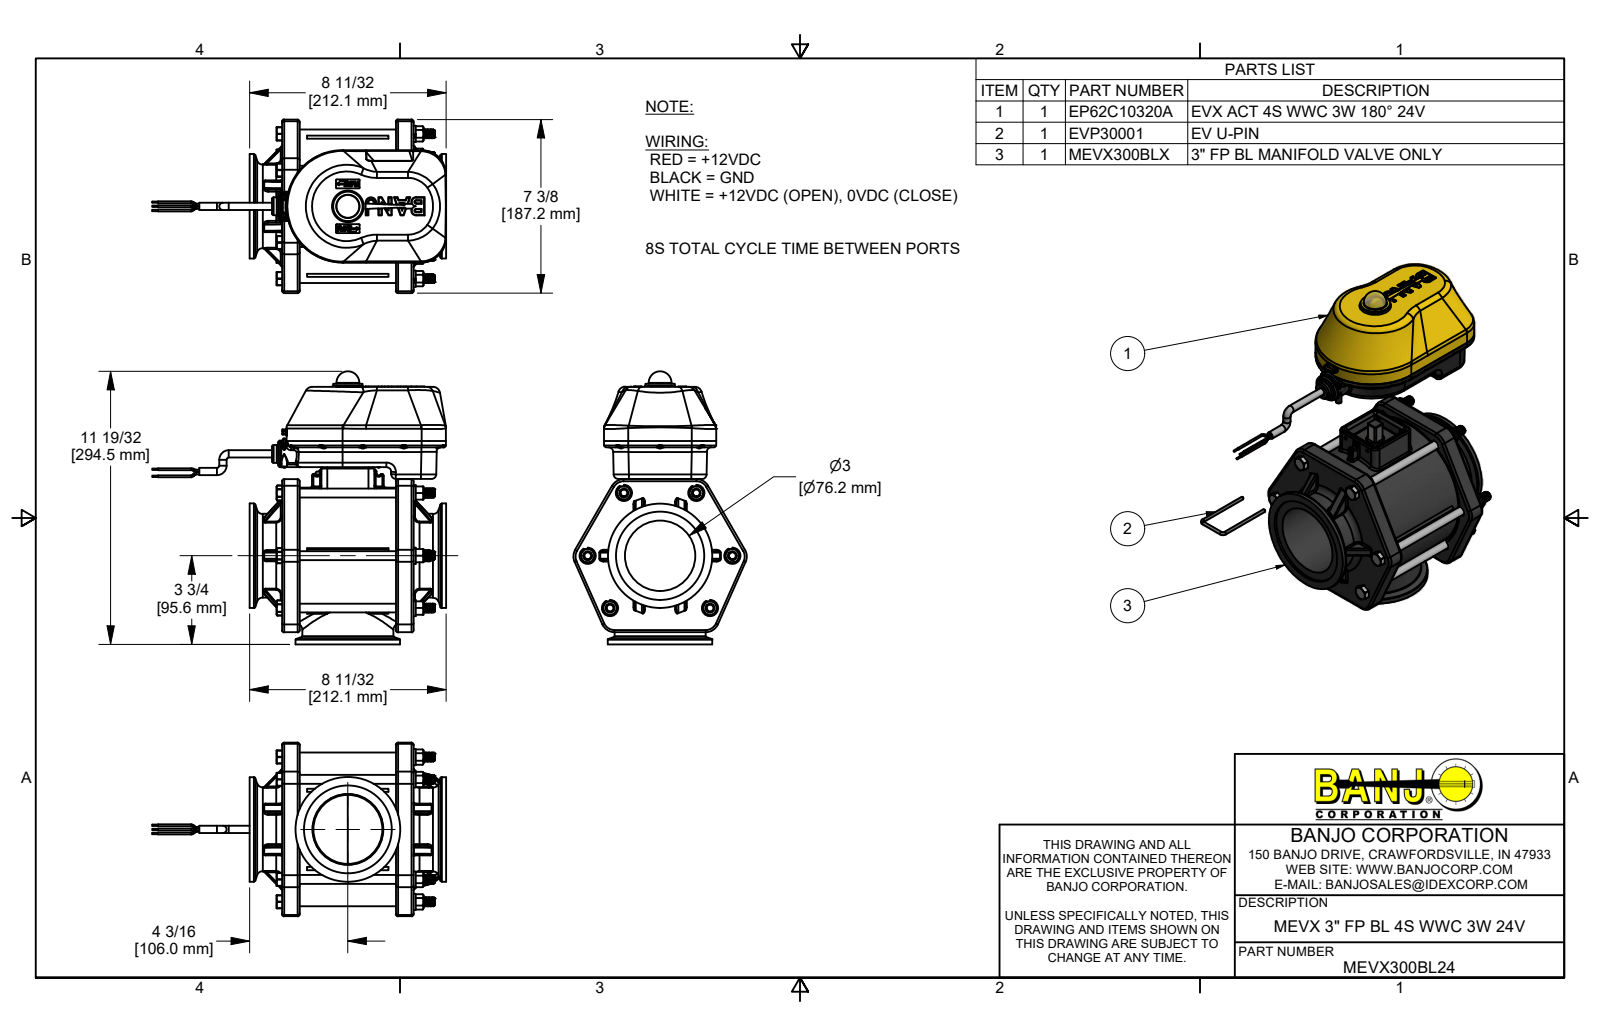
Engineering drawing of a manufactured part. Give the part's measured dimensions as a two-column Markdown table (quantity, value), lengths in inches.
| quantity | value |
| --- | --- |
| part name | MEVX300BL24; MEVX300BLX; MEVX35254BL; MEVX35254BLX (+8 more) |
| STEP written by | Autodesk Inventor 2019 (AUTOMOTIVE_DESIGN) |
| units | inches |
| bodies | 98 solids, 8930 faces (3103 planar, 3556 cylindrical, 2271 other) |
| overall size | 12.486 × 11.594 × 7.37 |
| volume | 168.5 in³ |
| surface area | 1 198 in² |
| round holes (diameter × count) | 0.15 × 15, 0.095 × 11, 0.34 × 11, 0.44 × 8, 0.08 × 7, 0.307 × 6, 0.385 × 6, 0.104 × 4, 0.136 × 4, 0.148 × 4, 0.176 × 4, 0.266 × 4 |
| round bosses / shafts (diameter × count) | 0.25 × 19, 0.08 × 15, 0.14 × 11, 0.108 × 11, 0.085 × 11, 0.375 × 10, 0.687 × 6, 0.294 × 6 |
| partial cylindrical surfaces (radius × count) | 0.013 × 204, 0.405 × 138, 0.387 × 114, 0.309 × 112, 0.253 × 108, 0.609 × 106, 0.01 × 96, 0.06 × 58 |
| main face-to-face distances | 0.69, 4.9, 0.215, 0.5, 5.59, 0.06, 0.905, 4.685, 3.995, 0.083 |
| hole center spacings | 3.075, 2.417, 3.075, 5.917, 4.263, 4.92, 5.655, 6.372 |
